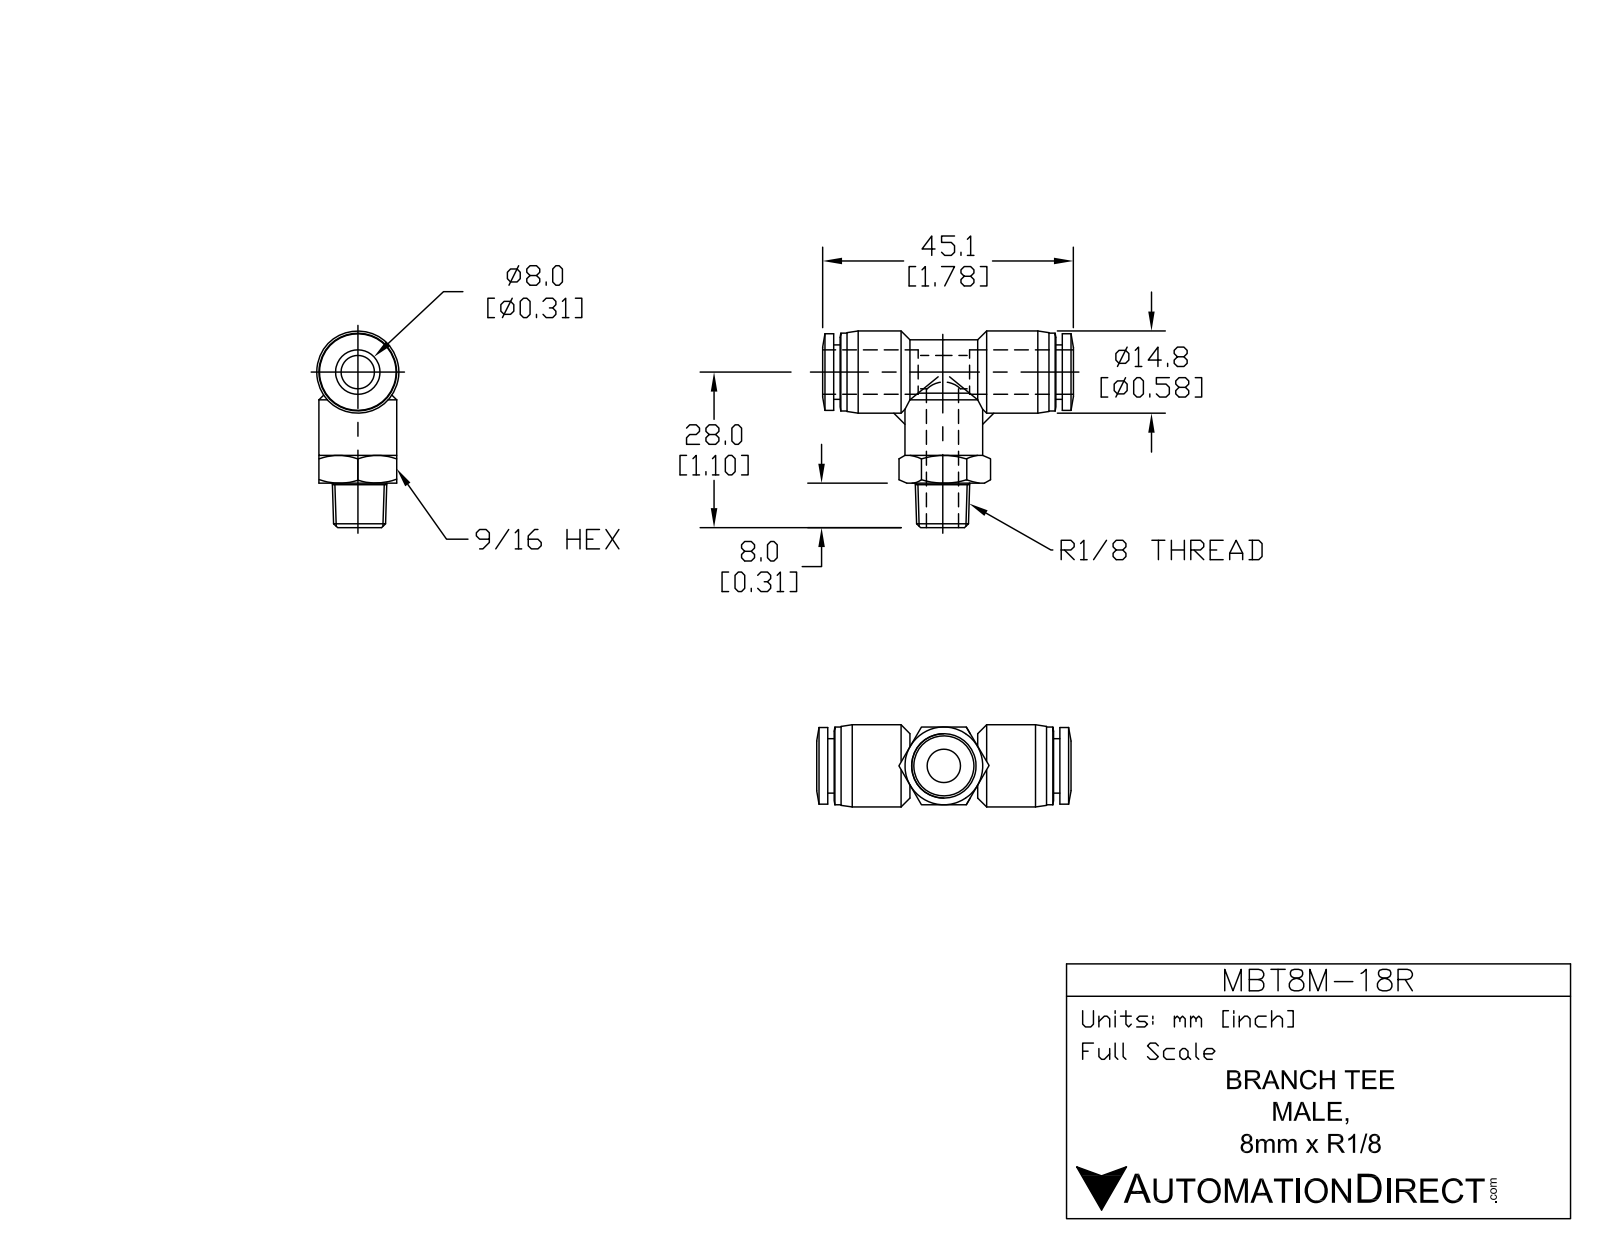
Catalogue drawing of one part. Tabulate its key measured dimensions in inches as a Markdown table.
| quantity | value |
| --- | --- |
| part name | MBT8M-18R |
| STEP written by | SolidWorks 2015 (AUTOMOTIVE_DESIGN) |
| units | inches |
| bodies | 1 solid, 99 faces (24 planar, 33 cylindrical, 42 other) |
| overall size | 1.78 × 1.398 × 0.591 |
| volume | 0.4 in³ |
| surface area | 7.79 in² |
| round holes (diameter × count) | 0.236 × 2, 0.327 × 1 |
| round bosses / shafts (diameter × count) | 0.551 × 2, 0.591 × 1, 0.555 × 1, 0.547 × 1, 0.543 × 1, 0.457 × 1, 0.39 × 1, 0.386 × 1 |
| partial cylindrical surfaces (radius × count) | 0.228 × 1 |
| main face-to-face distances | 0.551, 0.045, 1.577, 1.622, 1.531, 0.315, 0.642, 0.596, 0.935, 0.98 |
